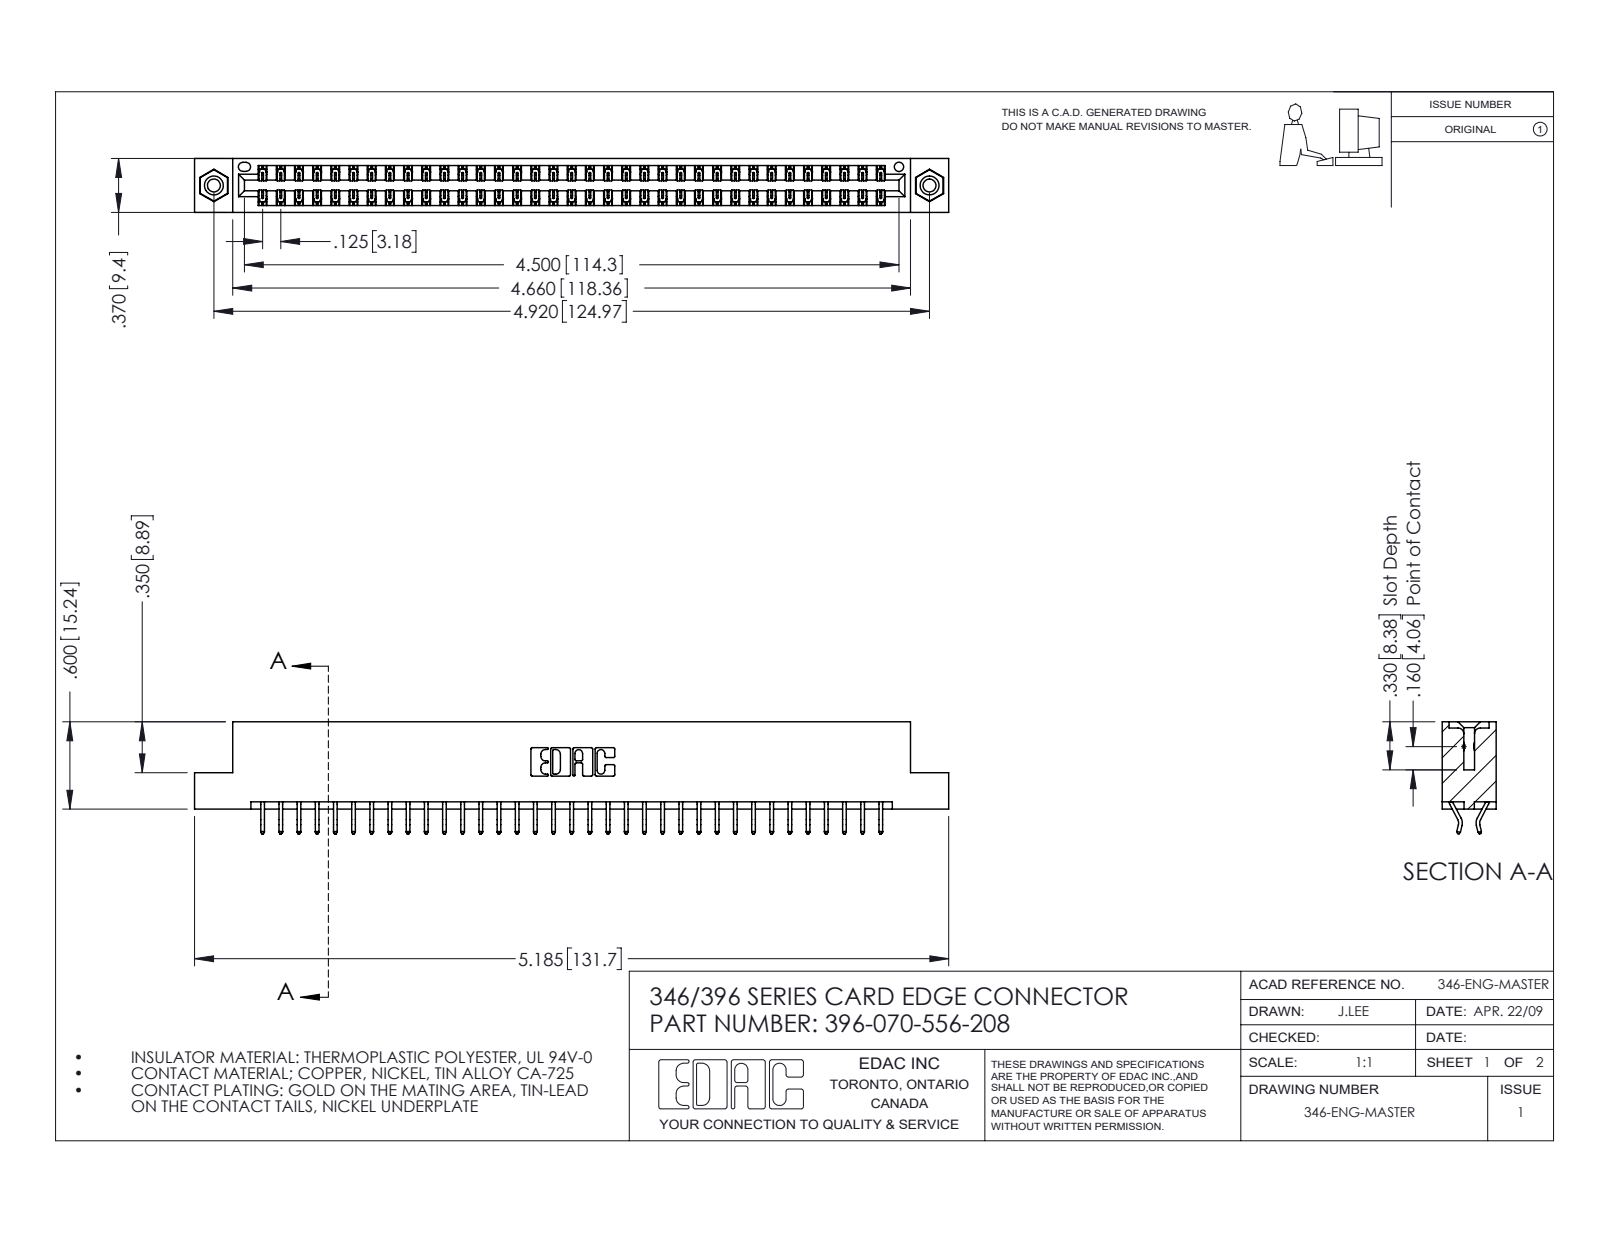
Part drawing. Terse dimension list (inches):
name: 346 Part_Flush Mounting Lugs - 0.156 Dia-TI; 396-070-556-208; 345-250-001_345-250-003-102; 345-292-001_556 Tail
written by: SolidWorks 2016 (CONFIG_CONTROL_DESIGN)
unit: in
bodies: 73 solids, 4242 faces (2838 planar, 1388 cylindrical, 16 other)
size: 5.185 × 0.77 × 0.37
volume: 0.78 in³; area: 26.99 in²
holes: 2× ⌀0.089, 2× ⌀0.125, 2× ⌀0.156, 1× ⌀0.064
bosses: 2× ⌀0.155
rounds: 105× R0.006, 22× R0.01, 6× R0.007, 6× R0.031, 3× R0.026, 2× R0.01, 2× R0.014, 2× R0.022
face distances: 0.048, 0.322, 0.37, 0.25, 0.025, 0.072, 0.298, 0.275, 0.148, 0.222
hole spacings: 0.246, 4.711, 4.92
